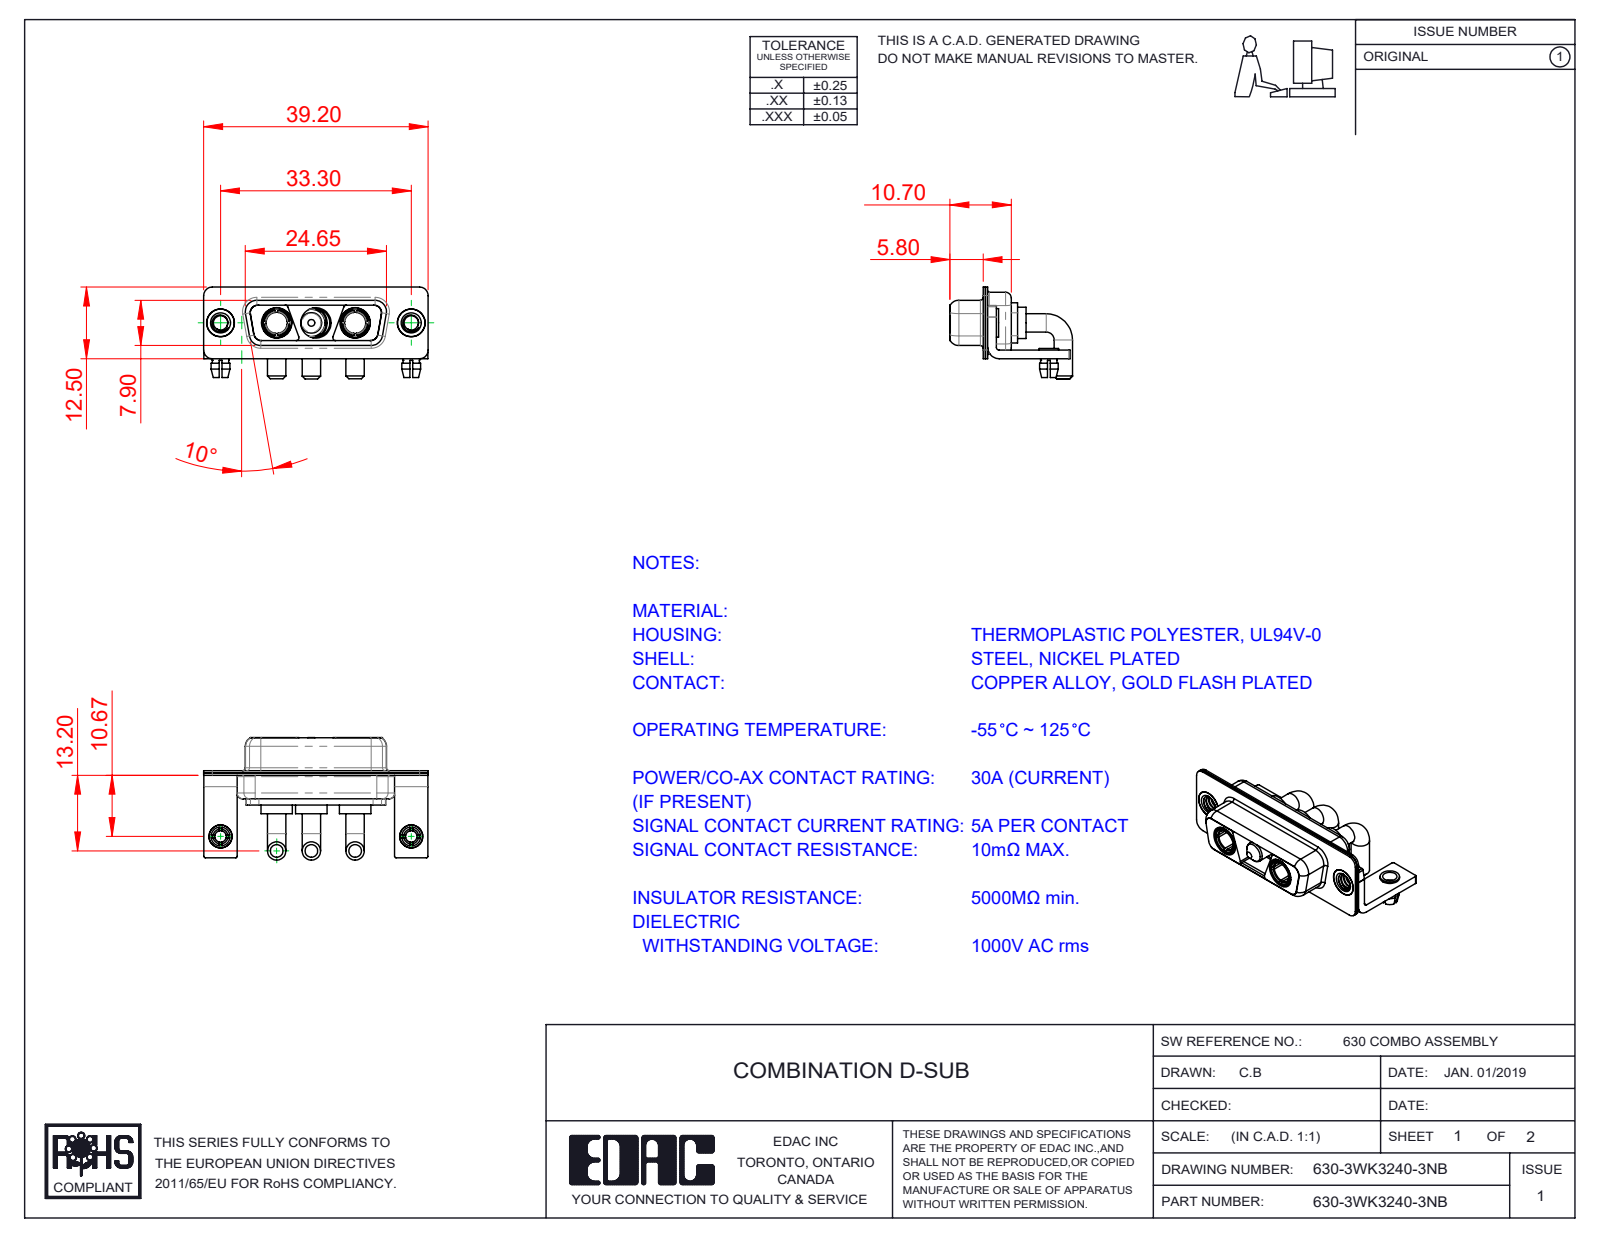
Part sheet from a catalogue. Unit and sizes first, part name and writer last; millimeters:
Units: millimetres
Overall size (bounding box): 39.2 × 21.4 × 16.05
Round holes (diameter × count): ⌀4.85 ×5, ⌀2.5 ×4, ⌀5.3 ×3, ⌀2 ×2, ⌀3.2 ×2, ⌀3.7 ×2, ⌀4 ×2, ⌀4.05 ×2
Round bosses / shafts (diameter × count): ⌀3.2 ×6, ⌀5.5 ×3, ⌀5.2 ×3, ⌀4.75 ×3, ⌀3.75 ×3, ⌀5 ×2, ⌀4.96 ×2, ⌀4.95 ×2
Partial cylindrical surfaces — rounded edges, fillets, slot ends (radius × count): R0.25 ×16, R1.5 ×16, R2 ×13, R1.35 ×12, R0.5 ×9, R1.6 ×8, R0.6 ×4, R0.65 ×4
Main face-to-face distances: 0.4, 0.8, 1.4, 1.5, 0.45, 8.45, 1.8, 8.9, 7.05, 5.2
Hole centre spacings: 6.85, 9.8, 16.65, 23.5, 33.3, 13.7
Volume: 2 877 mm³ · Surface area: 6 545 mm²
Bodies: 15 solids, 618 faces (208 planar, 263 cylindrical, 147 other)
Part name (STEP PRODUCT): 630Combo Stabilizer Bracket; 630-3WK3240-3NB; Power Socket_30A RA; 630Combo Housing_3WK3 (+5 more)
STEP written by: SolidWorks 2020 (CONFIG_CONTROL_DESIGN)
